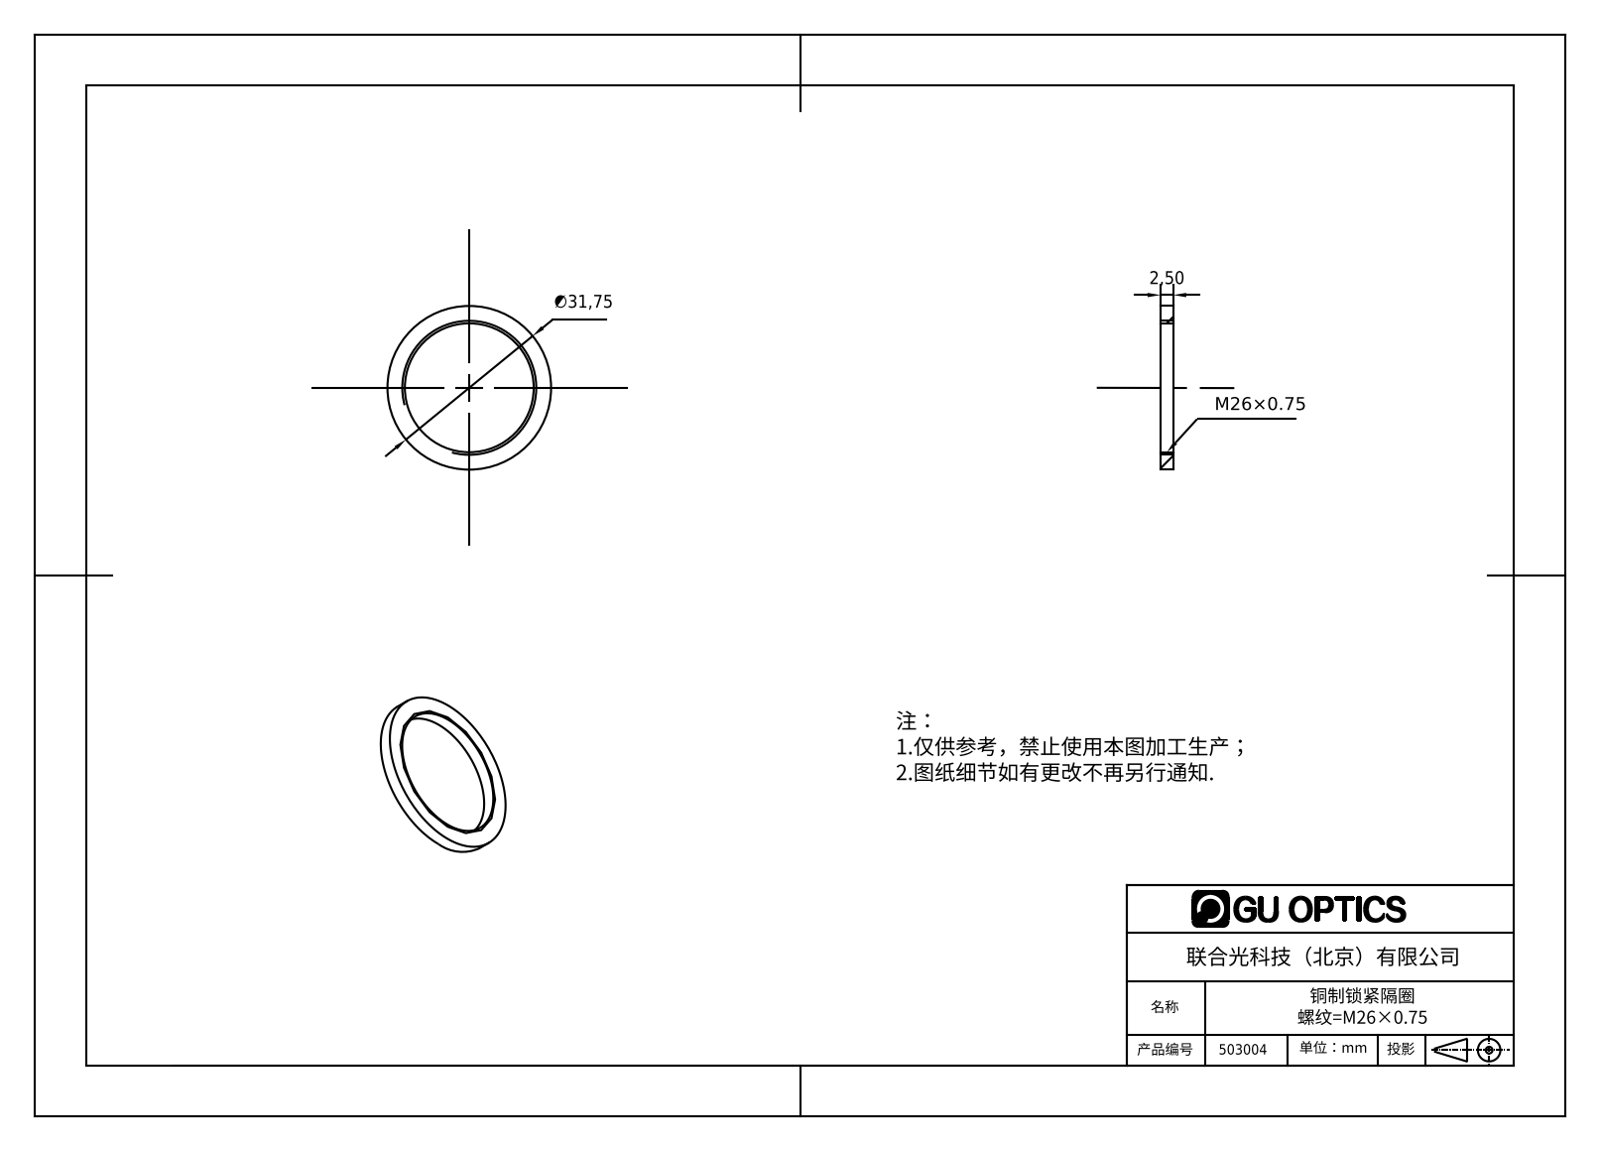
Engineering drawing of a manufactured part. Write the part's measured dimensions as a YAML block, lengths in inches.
part_name: "511004"
step_written_by: "SolidWorks 2016 (AUTOMOTIVE_DESIGN)"
units: inches
bodies: {solids: 1, faces: 6, planar: 2, cylindrical: 4, other: 0}
overall_size: [1.25, 1.25, 0.098]
volume: 0.046
surface_area: 1.623
round_holes:
  - {diameter: 0.984, count: 1}
round_bosses_or_shafts:
  - {diameter: 1.25, count: 1}
face_to_face_distances: [0.098]
